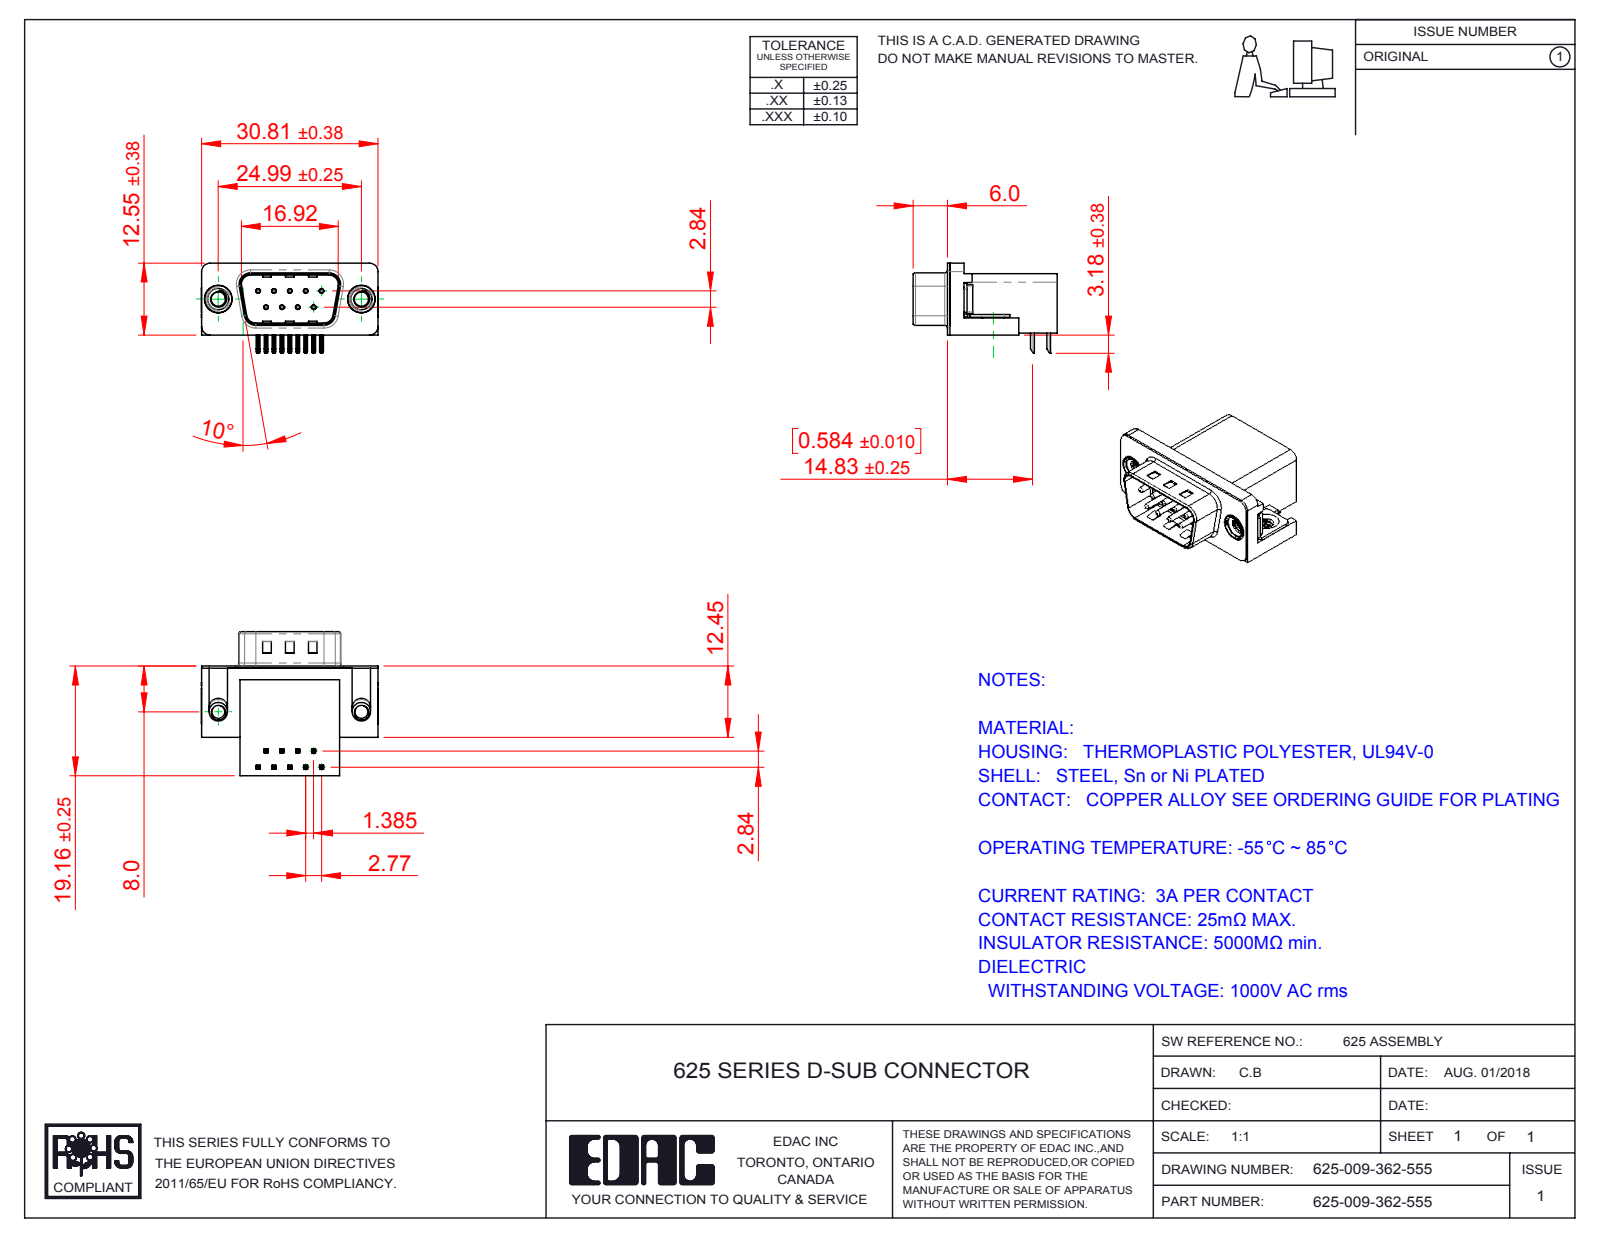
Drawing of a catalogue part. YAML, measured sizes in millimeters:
part_name: "625 Contact Top; 625 4-40 Threaded Board Mount; 625 Shell_9 Socket; 625-009-362-555 (+3 more)"
step_written_by: "SolidWorks 2016 (CONFIG_CONTROL_DESIGN)"
units: millimeters
bodies: {solids: 15, faces: 1025, planar: 575, cylindrical: 333, other: 117}
overall_size: [30.89, 25.16, 15.73]
volume: 4481
surface_area: 5034
round_holes:
  - {diameter: 0.35, count: 9}
  - {diameter: 0.8, count: 9}
  - {diameter: 2.26, count: 2}
  - {diameter: 2.5, count: 2}
  - {diameter: 4, count: 2}
  - {diameter: 4.8, count: 2}
  - {diameter: 5, count: 2}
round_bosses_or_shafts:
  - {diameter: 0.75, count: 9}
  - {diameter: 4.9, count: 2}
  - {diameter: 4.75, count: 2}
  - {diameter: 3.9, count: 2}
  - {diameter: 3.26, count: 2}
partial_cylinders:
  - {radius: 0.25, count: 44}
  - {radius: 0.12, count: 18}
  - {radius: 1, count: 16}
  - {radius: 0.5, count: 9}
  - {radius: 1.5, count: 8}
  - {radius: 1.6, count: 8}
  - {radius: 0.9, count: 4}
  - {radius: 2, count: 4}
face_to_face_distances: [0.4, 10.34, 18.76, 19.16, 2.9, 16.26, 2.5, 0.35, 10.69, 6.7]
hole_center_spacings: [3.16, 2.77, 5.54, 5.03, 5.04, 8.31, 7.48, 7.49]
